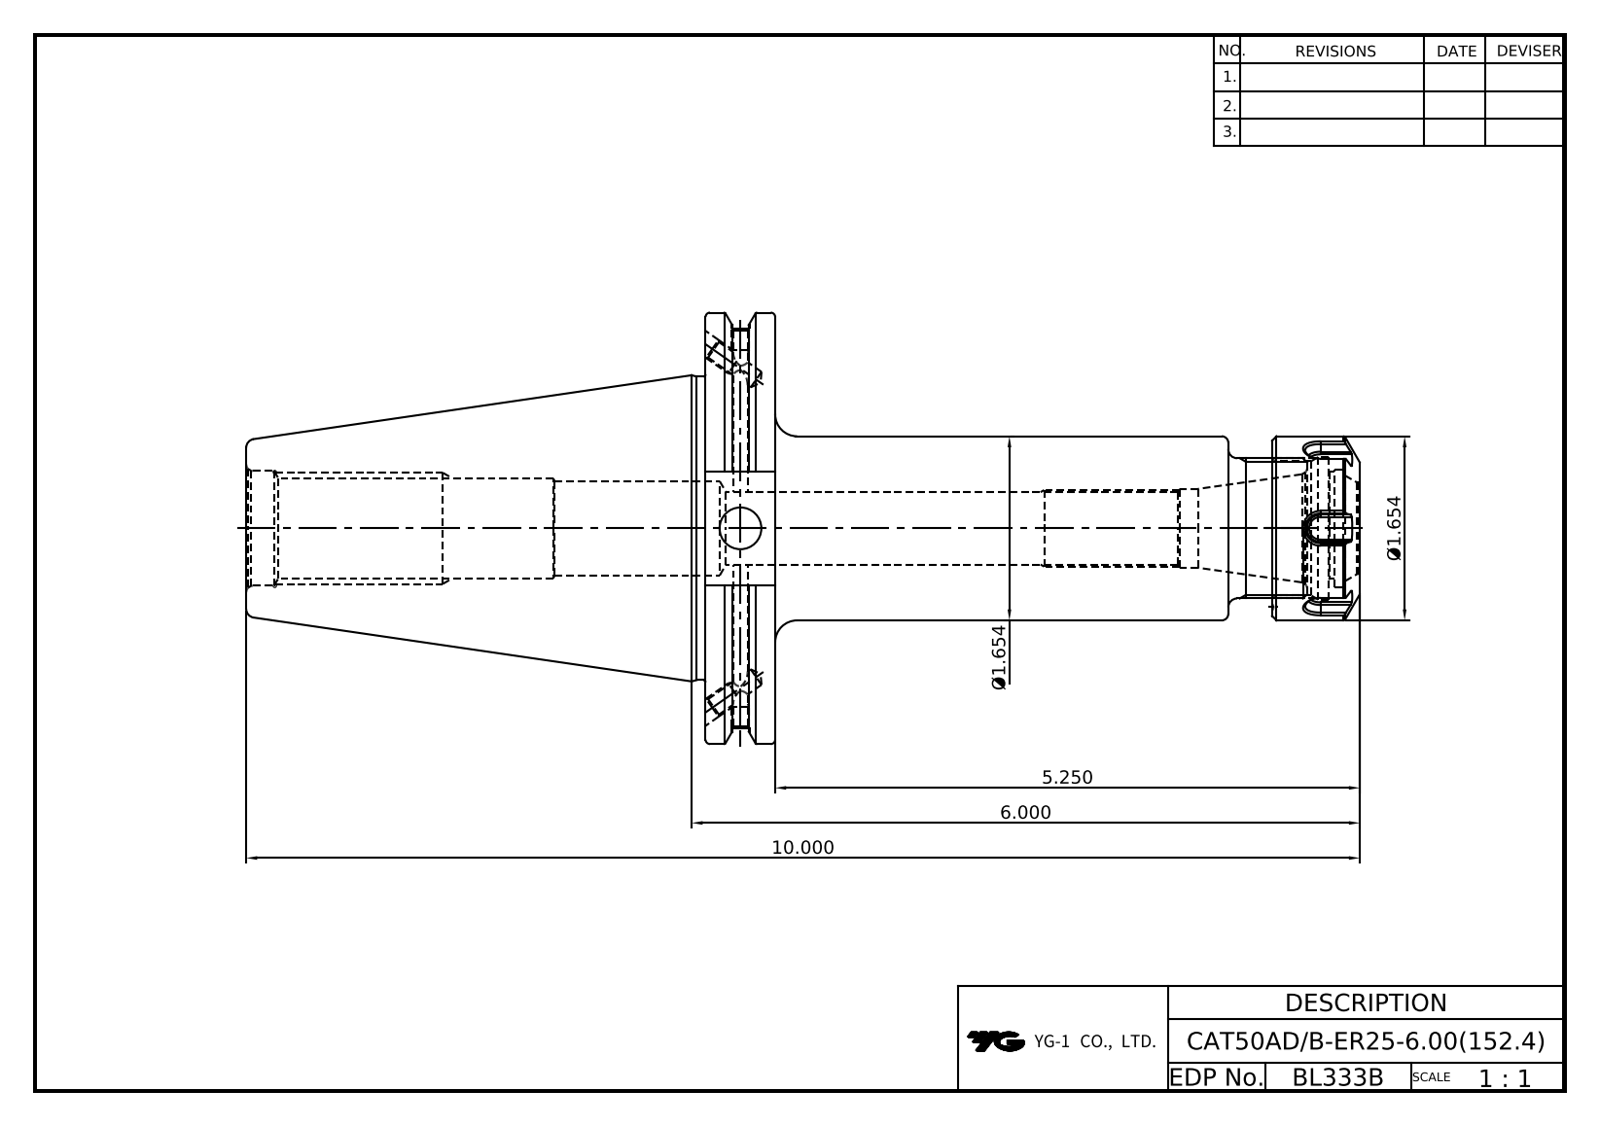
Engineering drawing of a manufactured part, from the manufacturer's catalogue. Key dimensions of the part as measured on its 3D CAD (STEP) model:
Part name (STEP PRODUCT): LO-CAT50ADB-ER25-152.4_조립도; LO-CAT50ADB-ER25-152.4; ER25NUT
STEP written by: Autodesk Inventor 2022 (AUTOMOTIVE_DESIGN)
Units: millimetres
Bodies: 2 solids, 170 faces (73 planar, 45 cylindrical, 52 other)
Overall size (bounding box): 254 × 98.42 × 94.69
Volume: 462 426 mm³ · Surface area: 72 985 mm²
Round holes (diameter × count): ⌀3.24 ×2, ⌀4.13 ×2, ⌀4.2 ×2, ⌀5 ×2, ⌀9.53 ×1, ⌀15.75 ×1, ⌀18 ×1, ⌀20.9 ×1, ⌀21.5 ×1, ⌀21.97 ×1, ⌀23 ×1, ⌀26.2 ×1
Round bosses / shafts (diameter × count): ⌀98.42 ×1, ⌀91.29 ×1, ⌀69.25 ×1, ⌀42 ×1, ⌀32 ×1
Partial cylindrical surfaces — rounded edges, fillets, slot ends (radius × count): R0.5 ×12
Main face-to-face distances: 15.88, 104.77, 120.65, 234, 129.23, 113.35, 246.9, 142.13, 126.25, 12.9
